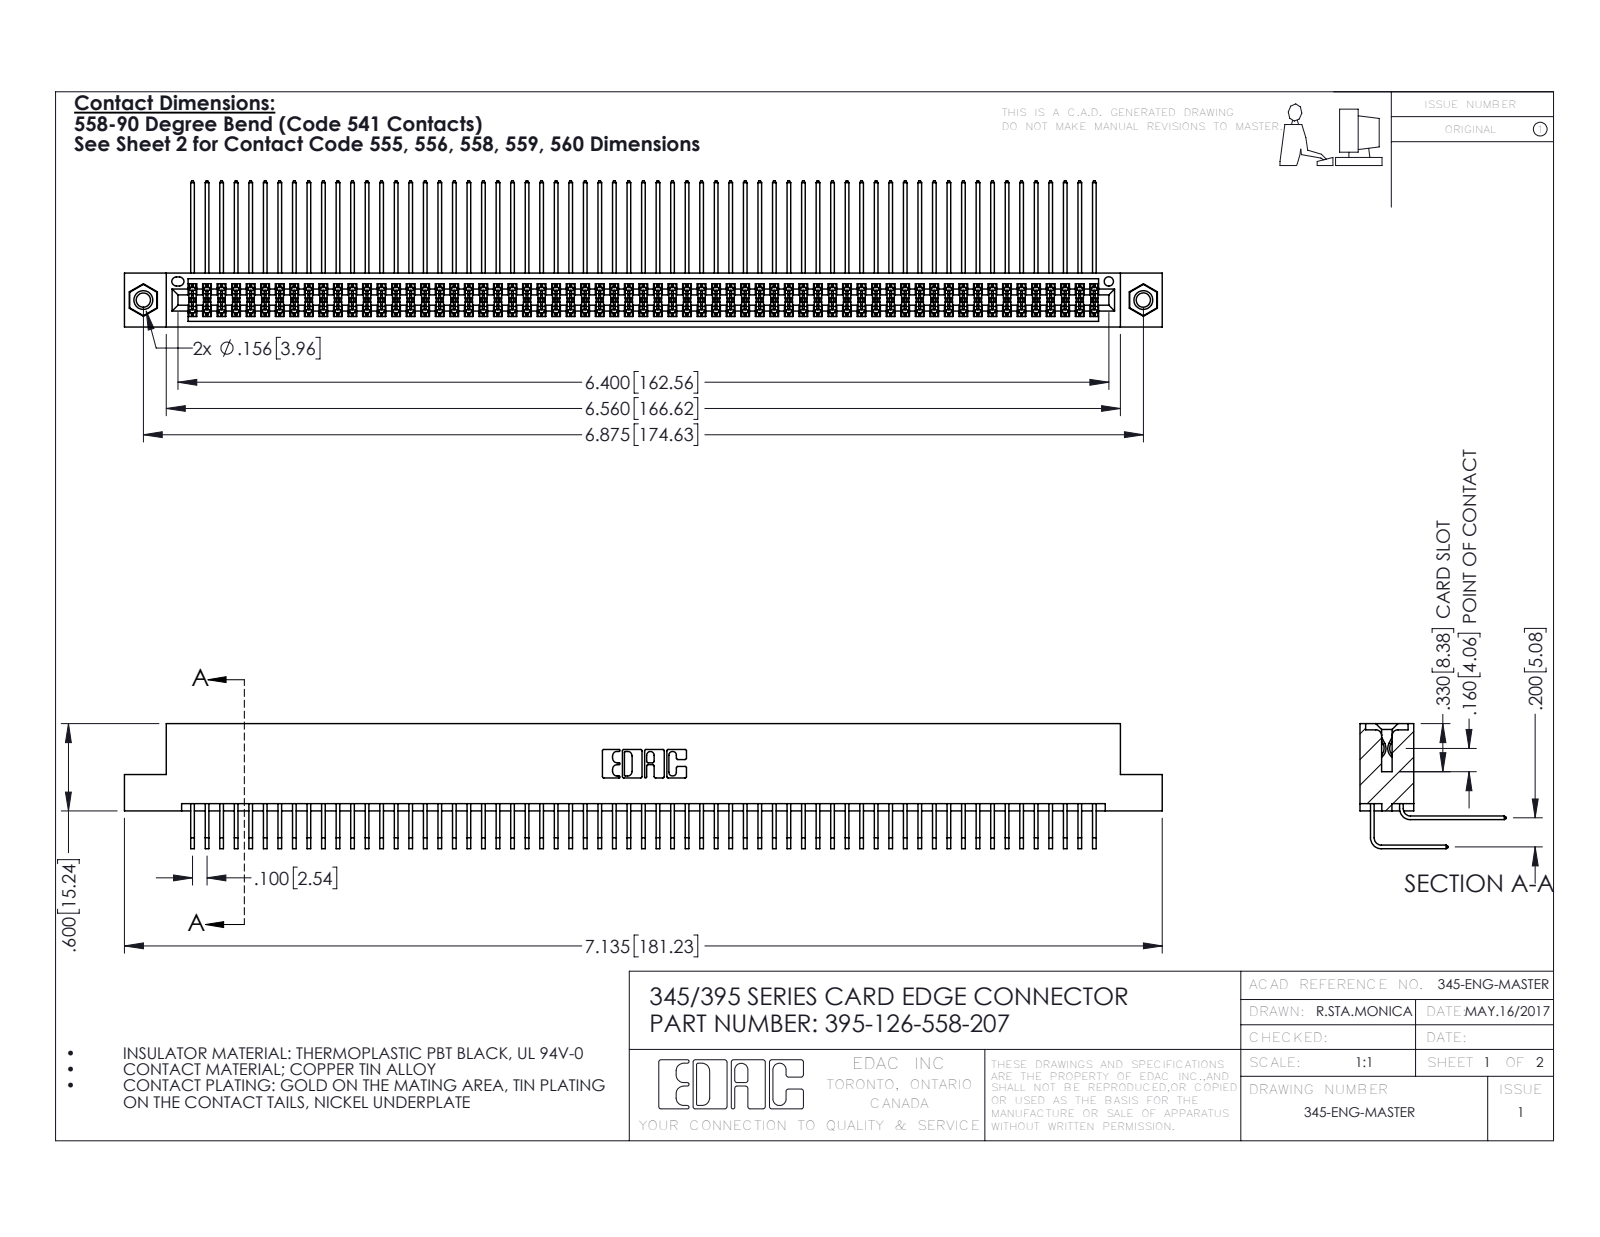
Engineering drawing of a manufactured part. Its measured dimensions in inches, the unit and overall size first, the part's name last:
Units: inches
Overall size (bounding box): 7.135 × 1.005 × 0.859
Round holes (diameter × count): ⌀0.098 ×2, ⌀0.125 ×2, ⌀0.156 ×2, ⌀0.064 ×1
Round bosses / shafts (diameter × count): ⌀0.155 ×2
Partial cylindrical surfaces — rounded edges, fillets, slot ends (radius × count): R0.006 ×190, R0.01 ×22, R0.007 ×6, R0.031 ×6, R0.026 ×3, R0.014 ×2, R0.019 ×2, R0.022 ×2
Main face-to-face distances: 0.072, 0.298, 0.2, 0.37, 0.098, 0.272, 0.025, 0.225, 0.025, 0.175
Hole centre spacings: 0.27, 6.639, 6.875
Volume: 1.13 in³ · Surface area: 48.39 in²
Bodies: 129 solids, 6738 faces (4522 planar, 2200 cylindrical, 16 other)
Part name (STEP PRODUCT): 345 Part_Flush Mounting Lugs - 0.156 Dia-TI; 395-126-558-207; 345-250-001_345-250-005-103; 345-292-001_558 559 Tail - 1 (+1 more)
STEP written by: SolidWorks 2016 (CONFIG_CONTROL_DESIGN)
